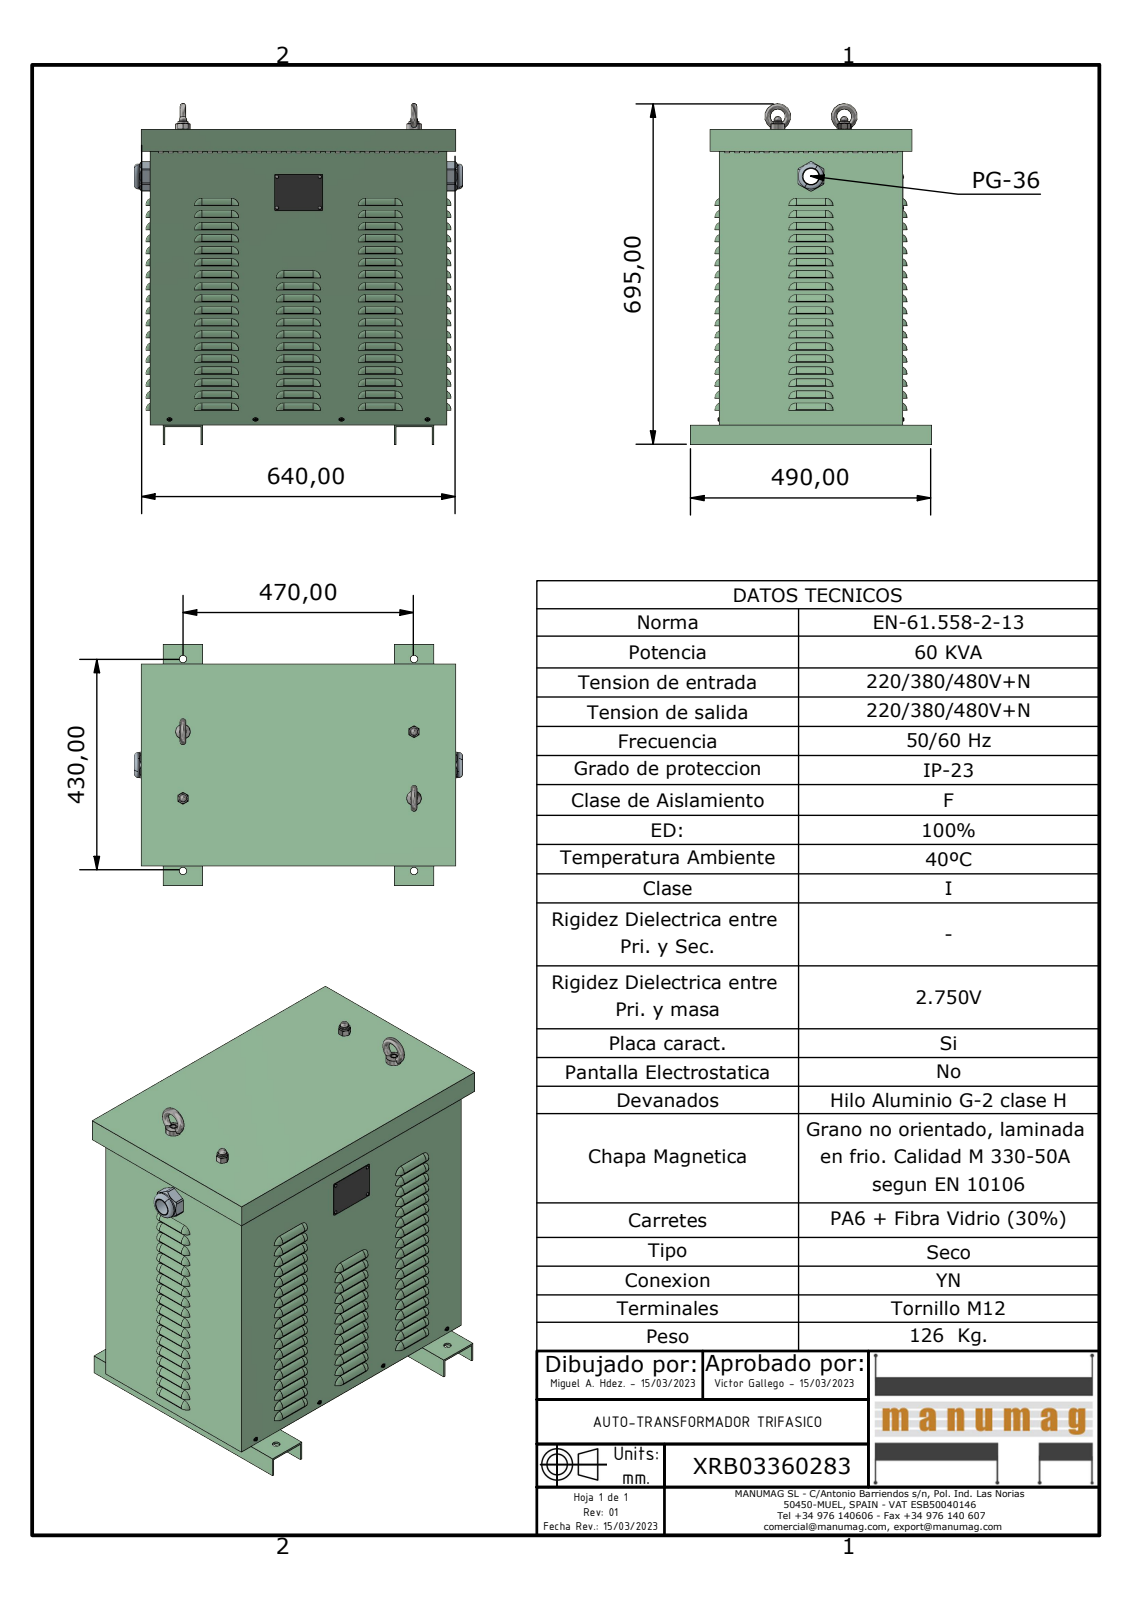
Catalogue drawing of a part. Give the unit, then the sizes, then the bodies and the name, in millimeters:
Units: millimetres
Overall size (bounding box): 695 × 668.2 × 490
Round holes (diameter × count): ⌀11 ×364, ⌀15 ×8, ⌀4 ×4, ⌀5 ×4, ⌀10.11 ×2, ⌀11.84 ×2, ⌀32 ×1, ⌀48 ×1
Round bosses / shafts (diameter × count): ⌀4 ×4, ⌀3.62 ×4, ⌀3.2 ×4, ⌀51.1 ×2, ⌀30 ×2, ⌀21 ×2, ⌀15.6 ×2, ⌀47.45 ×1
Partial cylindrical surfaces — rounded edges, fillets, slot ends (radius × count): R14 ×132, R7 ×72, R15 ×72, R3.88 ×12, R2.5 ×8, R7.5 ×8, R2 ×4, R30 ×2
Main face-to-face distances: 2, 370, 600, 601, 368, 372, 602, 599, 598, 603
Hole centre spacings: 30, 21.21, 132, 128.88, 147, 173.76, 279, 469.24
Volume: 4 615 000 mm³ · Surface area: 4 047 000 mm²
Bodies: 24 solids, 2907 faces (1145 planar, 1024 cylindrical, 738 other)
Part name (STEP PRODUCT): XRB03360283; JE060 - JE075 CUERPO; JE060 - JE075 BASE; JE060 TAPA SUPERIOR (+7 more)
STEP written by: Autodesk Inventor 2023 (AUTOMOTIVE_DESIGN)
